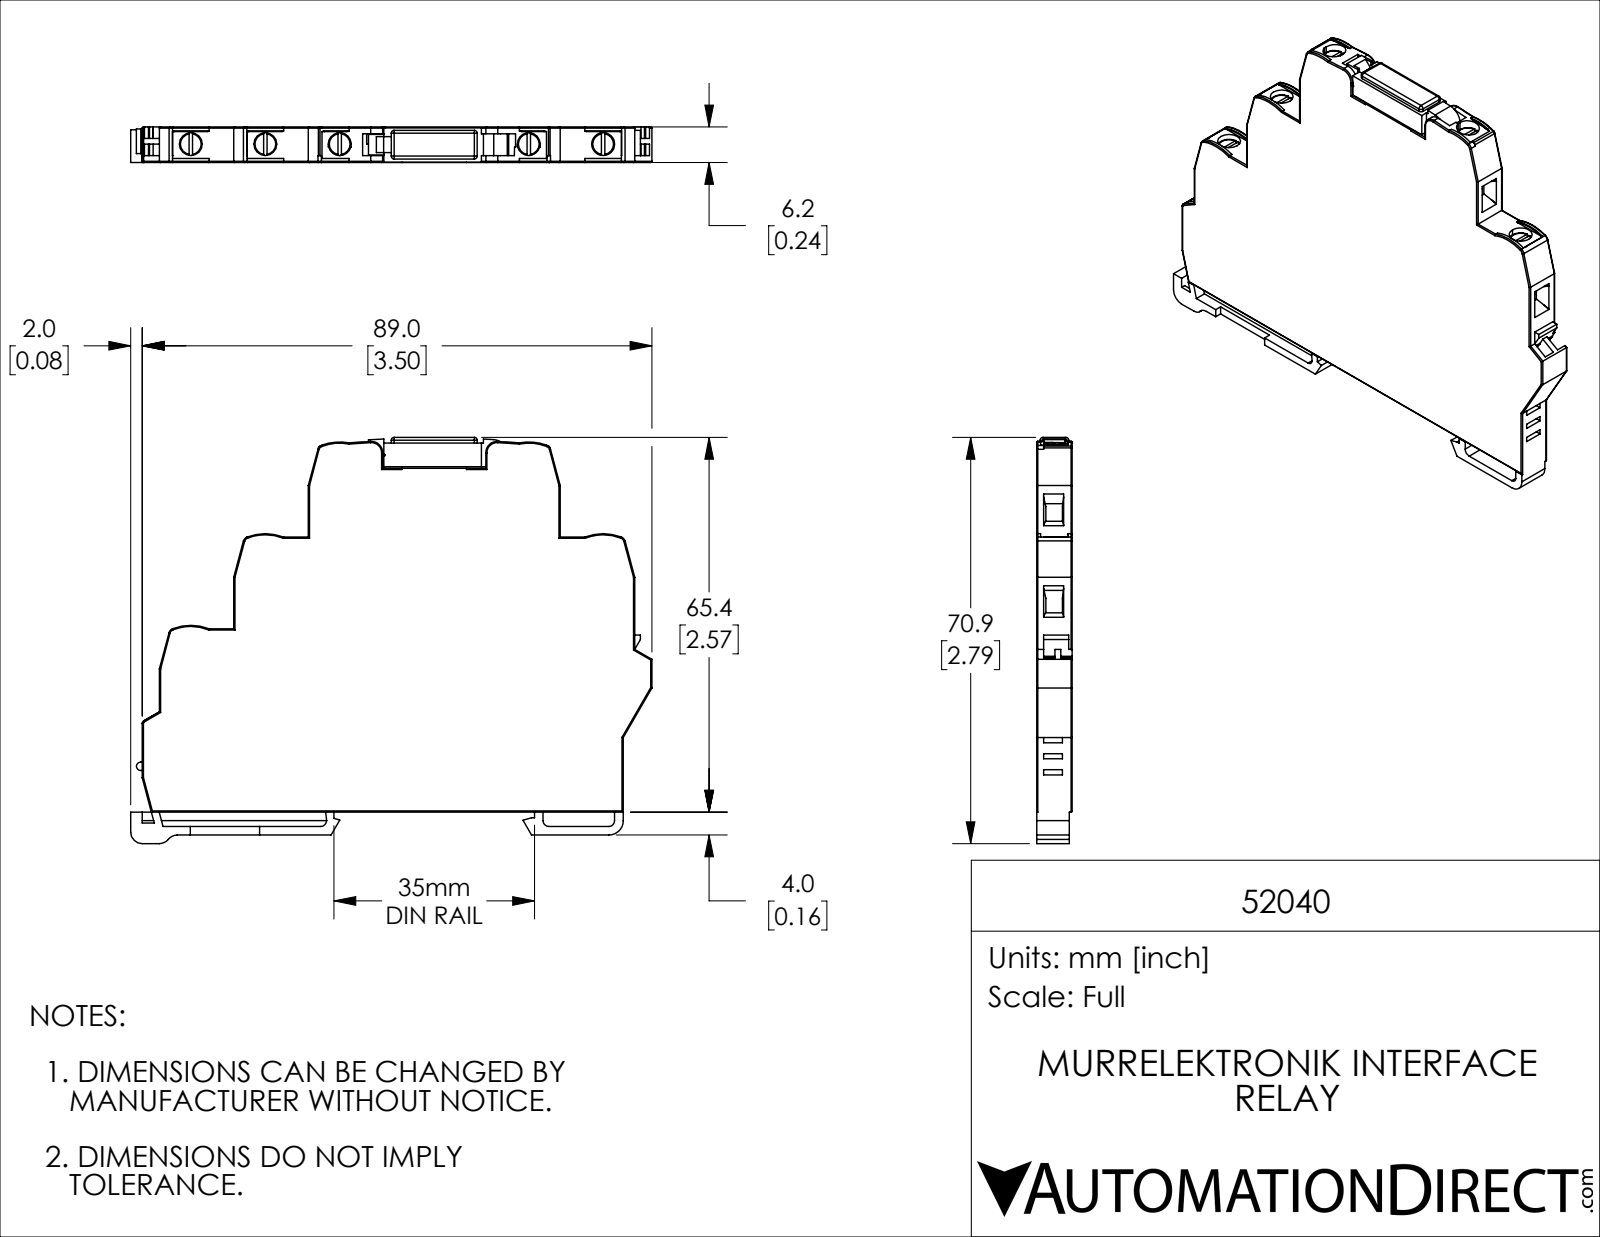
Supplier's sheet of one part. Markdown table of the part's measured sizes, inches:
| quantity | value |
| --- | --- |
| part name | 52040 |
| STEP written by | SolidWorks 2019 (CONFIG_CONTROL_DESIGN) |
| units | inches |
| bodies | 2 solids, 566 faces (351 planar, 147 cylindrical, 68 other) |
| overall size | 3.583 × 2.791 × 0.244 |
| volume | 1.706 in³ |
| surface area | 20.13 in² |
| round holes (diameter × count) | 0.157 × 5, 0.075 × 1 |
| round bosses / shafts (diameter × count) | 0.079 × 1 |
| partial cylindrical surfaces (radius × count) | 0.008 × 56, 0.02 × 11, 0.039 × 8, 0.079 × 6, 0.03 × 5, 0.346 × 5, 0.005 × 4, 0.016 × 3 |
| main face-to-face distances | 0.244, 0.059, 0.197, 0.098, 0.157, 0.118, 0.047, 0.02, 0.039, 2.362 |
| hole center spacings | 0.512, 1.811, 2.323, 1.024, 1.299, 2.835 |
